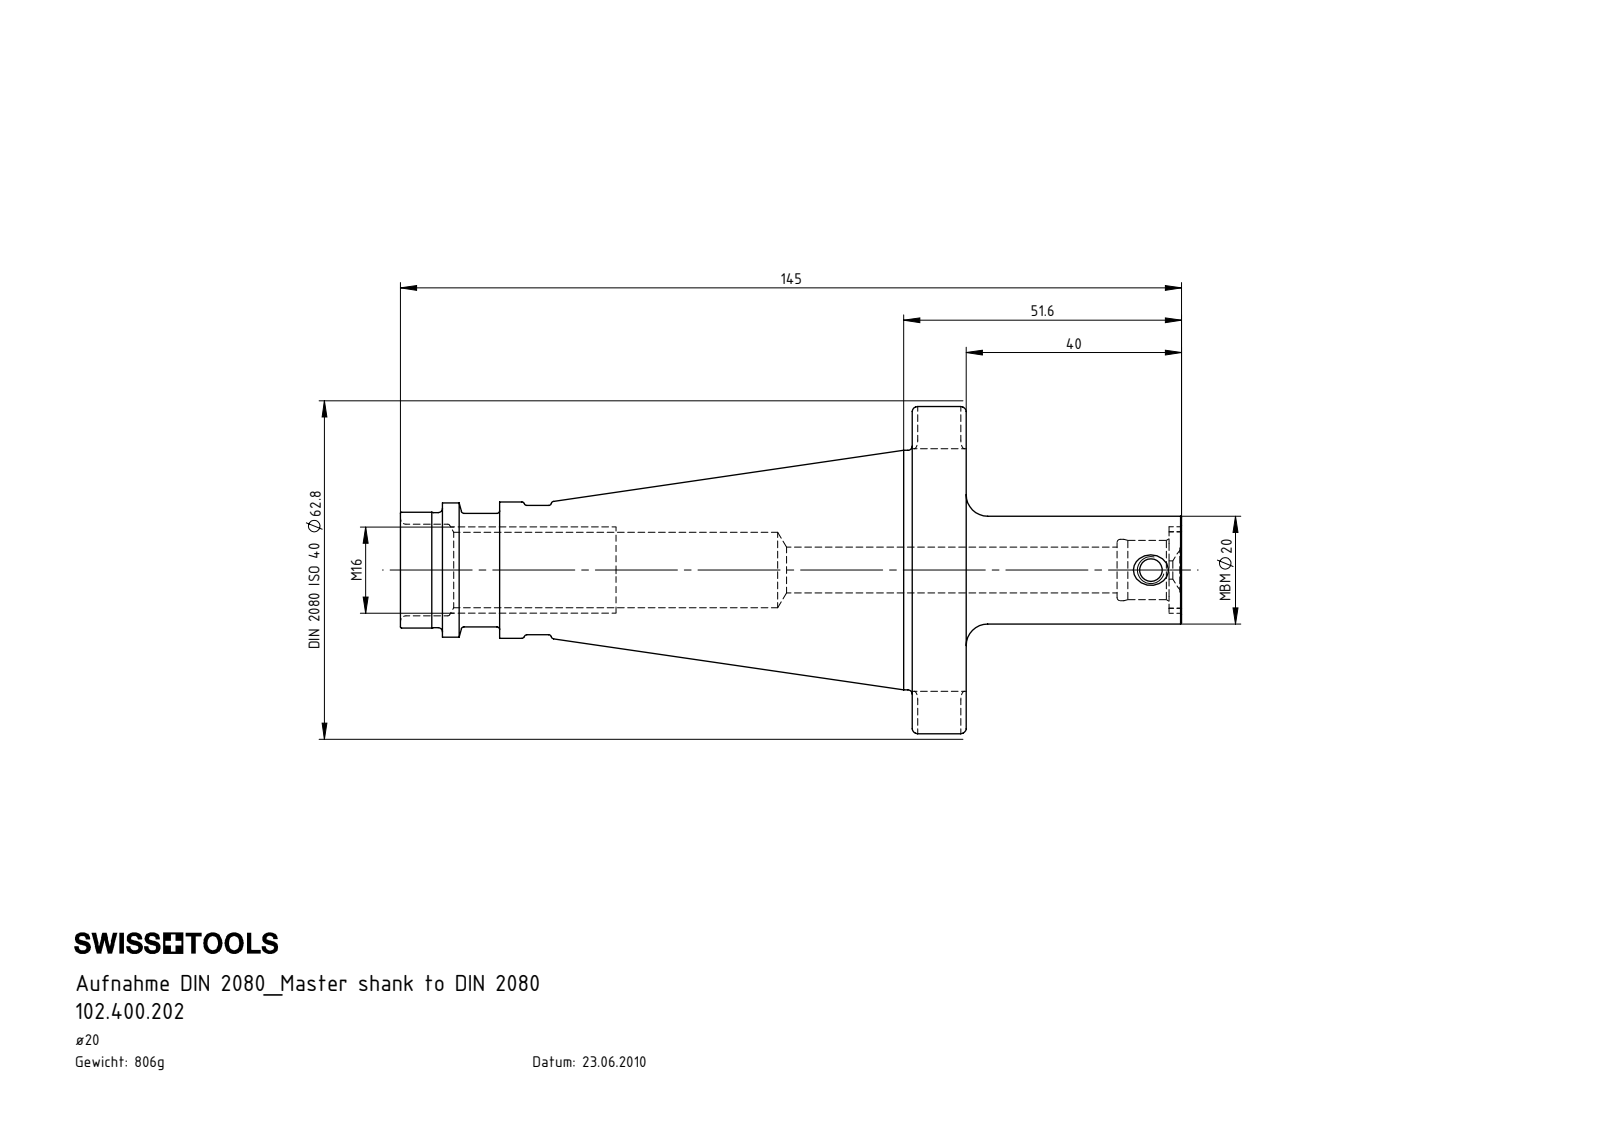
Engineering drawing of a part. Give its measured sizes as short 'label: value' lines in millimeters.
name: 102.400.202
written by: SolidWorks 2017 (CONFIG_CONTROL_DESIGN)
unit: mm
bodies: 1 solid, 141 faces (31 planar, 53 cylindrical, 57 other)
size: 145 × 62.8 × 60.7
volume: 102 654 mm³; area: 23 949 mm²
holes: 1× ⌀4.2, 1× ⌀8.5, 1× ⌀11, 1× ⌀11.4, 1× ⌀14, 1× ⌀17
bosses: 1× ⌀62.8, 1× ⌀44.45, 1× ⌀25.3, 1× ⌀24.91, 1× ⌀24, 1× ⌀21.5, 1× ⌀21.35, 1× ⌀21.05
rounds: 12× R1.6, 4× R2.2, 1× R6.5, 1× R8.03
face distances: 10, 45, 76.6, 86.6, 16.1, 126.6, 50, 40, 124.25, 47.65
